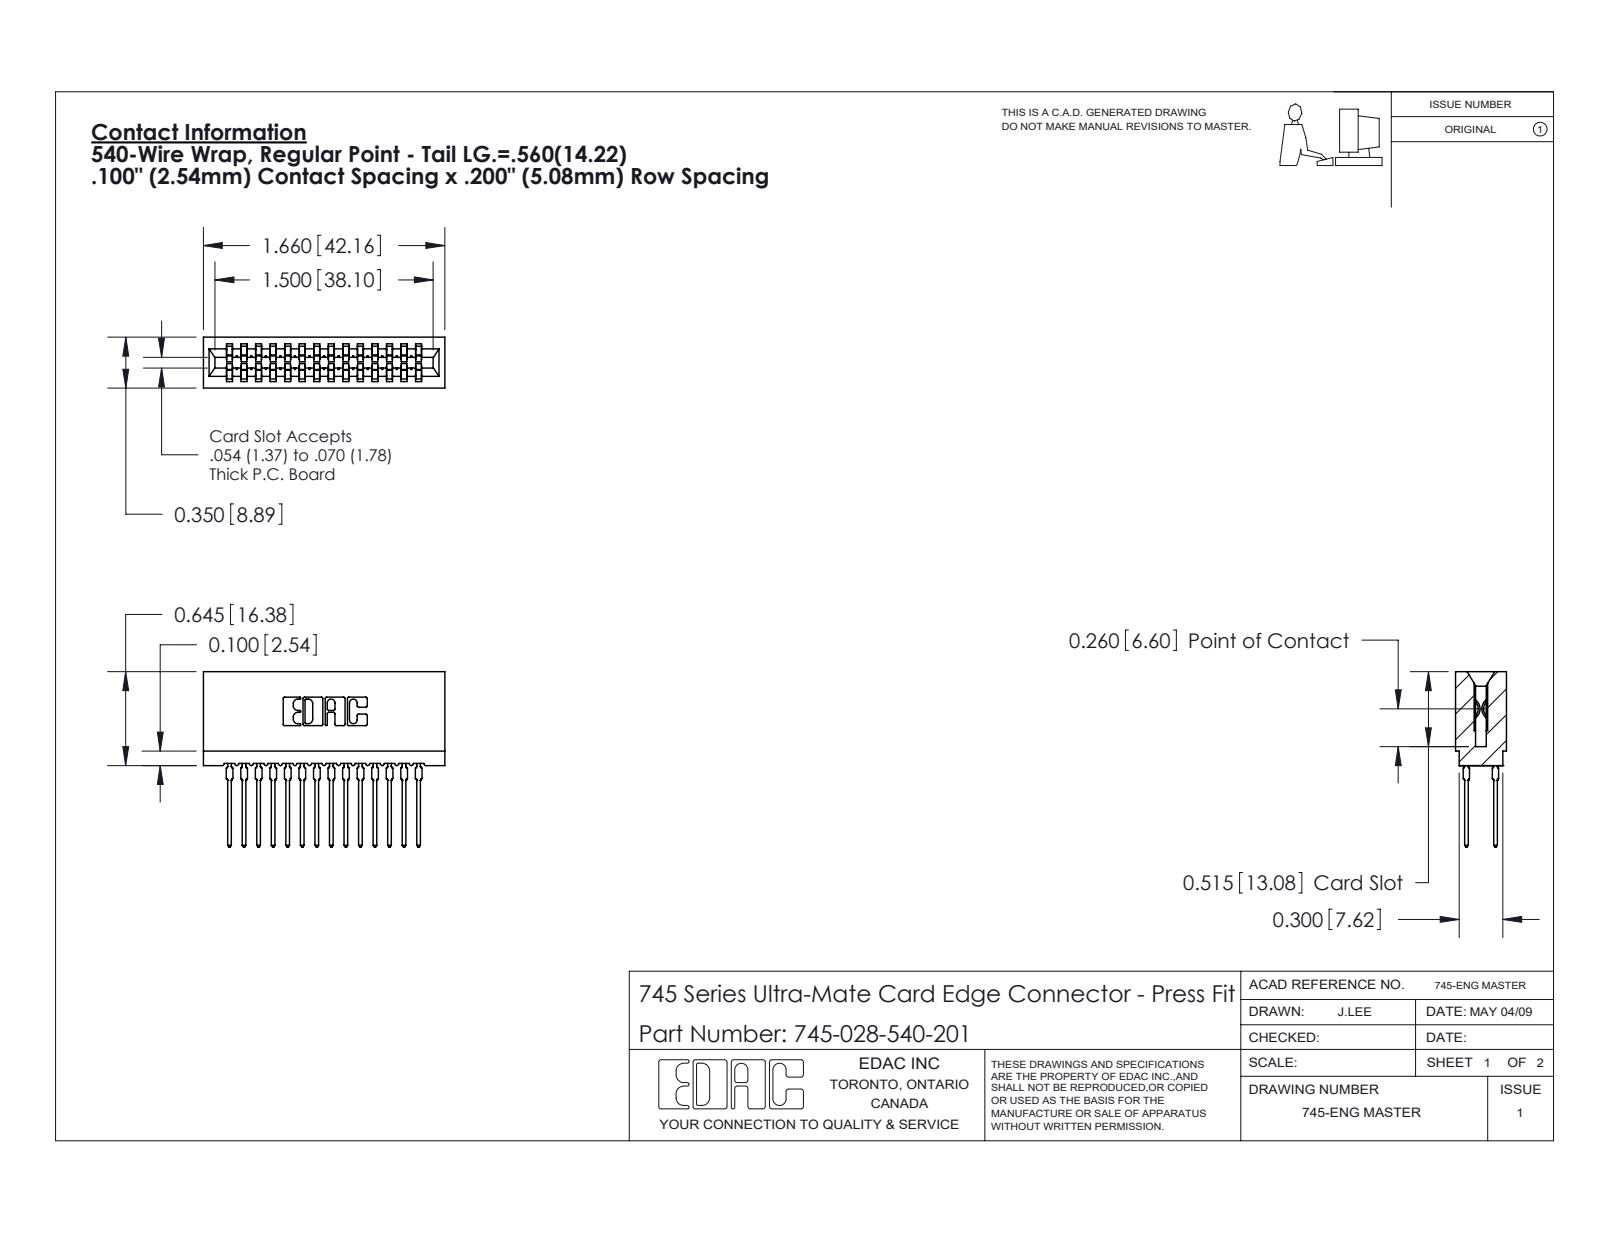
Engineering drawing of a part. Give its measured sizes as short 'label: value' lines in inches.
name: 745-028-540-201; 745-292-001_540; 745 Part_Insulator Option - 01
written by: SolidWorks 2020 (CONFIG_CONTROL_DESIGN)
unit: in
bodies: 29 solids, 2601 faces (1343 planar, 530 cylindrical, 728 other)
size: 1.66 × 1.206 × 0.35
volume: 0.247 in³; area: 12.26 in²
rounds: 56× R0.021, 28× R0.015, 22× R0.01, 8× R0.005, 8× R0.011, 6× R0.007, 6× R0.031, 3× R0.026
face distances: 0.2, 0.1, 0.3, 0.4, 0.5, 0.063, 0.287, 0.6, 0.35, 0.7
